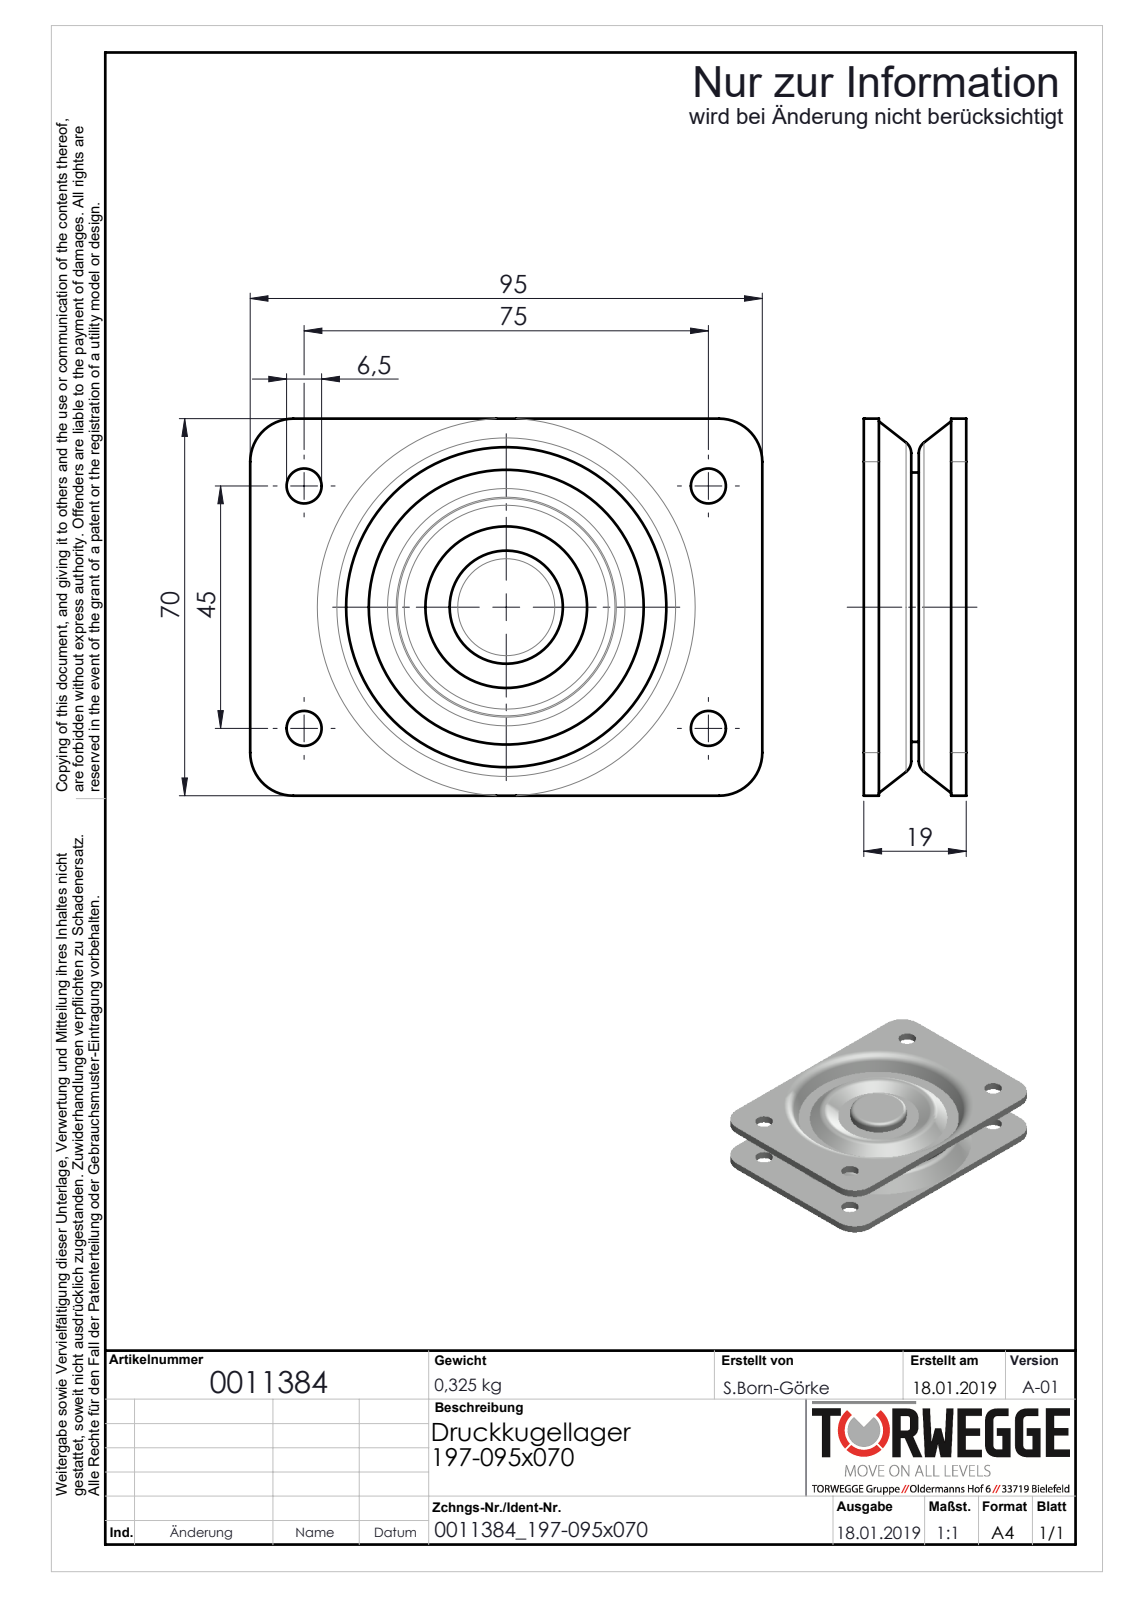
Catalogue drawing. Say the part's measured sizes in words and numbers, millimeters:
The part is named "0011384_197-095x070_(A-01)". Its 3-D file was written by "SolidWorks 2018 (AUTOMOTIVE_DESIGN)". It is 0 solids with 108 faces: 43 planar, 31 cylindrical and 34 other. Overall it measures 95 by 70 by 19 millimeters. Round holes: 4 of diameter 6.5. Round bosses or shafts: 1 of diameter 21, 1 of diameter 14.5. Partial cylindrical surfaces (rounded edges, fillets, slot ends): 4 of radius 8. The main face-to-face distances are 2.8, 6, 10.2, 8.8, 16.2, 7.4, 13.4, 19, 1.4, 5.1. The hole center spacings are 45, 75, 87.46.
